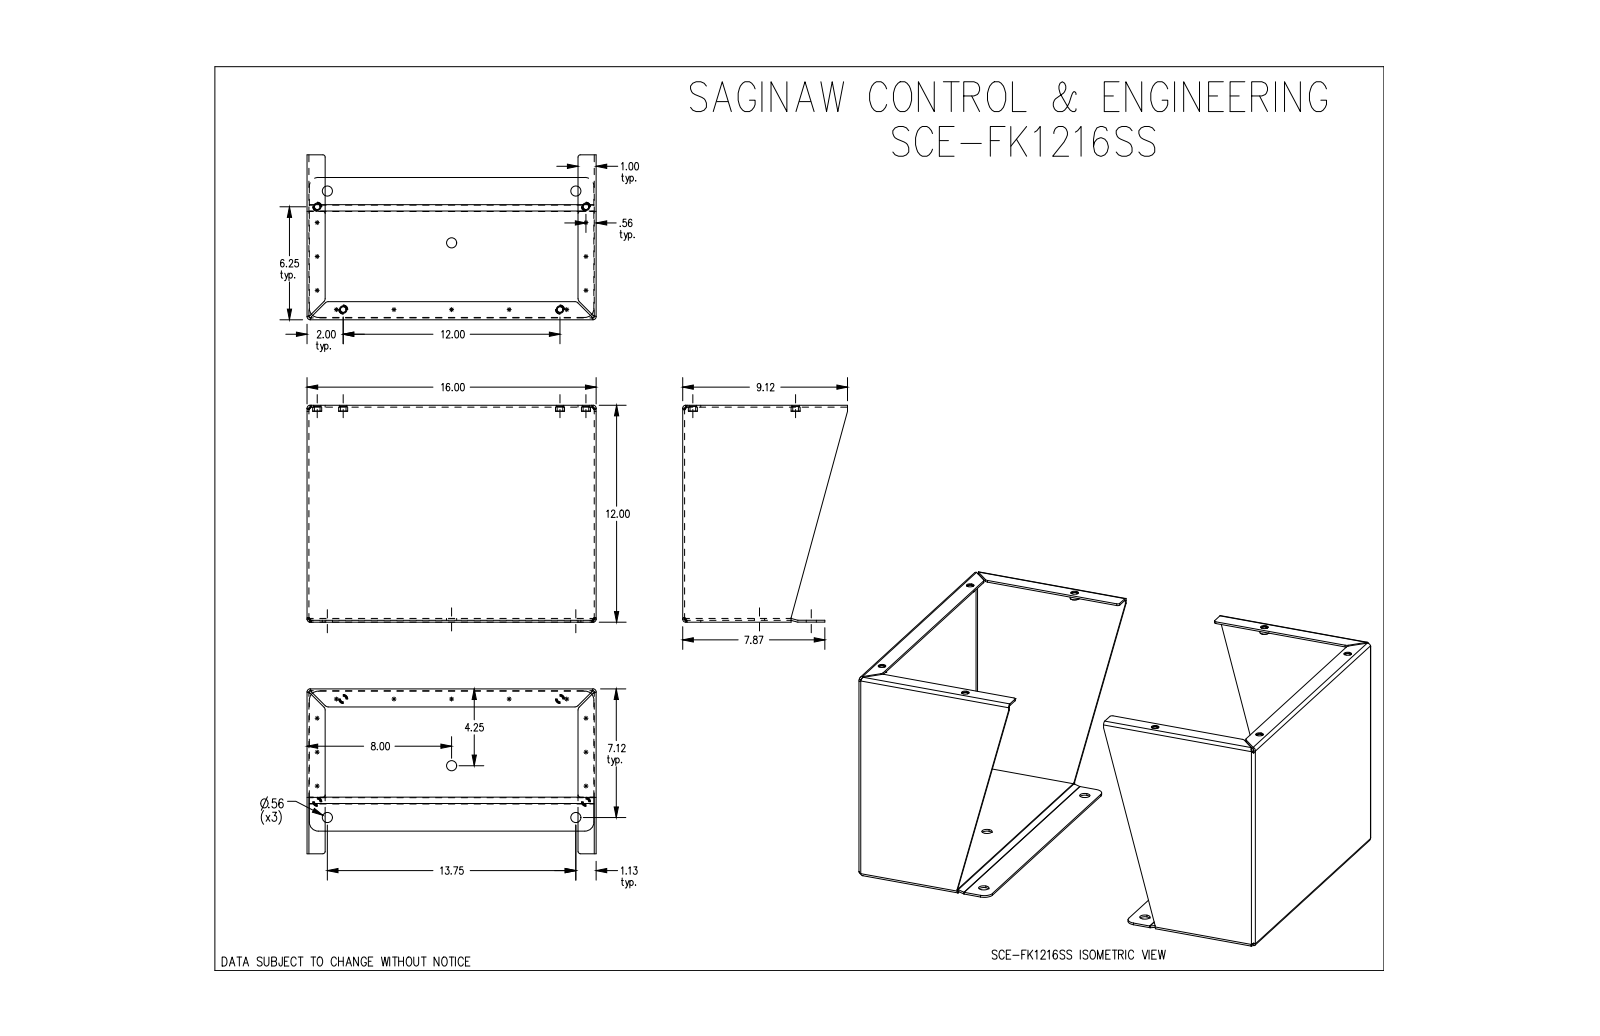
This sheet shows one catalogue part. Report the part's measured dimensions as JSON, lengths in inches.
{"part_name": "SCE-FK1216SS", "step_written_by": "SolidWorks 2019 (CONFIG_CONTROL_DESIGN)", "units": "inches", "bodies": {"solids": 12, "faces": 286, "planar": 120, "cylindrical": 110, "other": 56}, "overall_size": [24, 16, 12], "volume_in3": 112.3, "surface_area_in2": 2194, "round_holes": [[0.312, 8], [0.413, 8], [0.563, 6]], "round_bosses_or_shafts": [[0.5, 8], [0.412, 8]], "partial_cylinders_radius": [[0.166, 16], [0.062, 12], [0.125, 8], [0.22, 8], [0.5, 8], [0.063, 6]], "face_to_face_distances": [0.104, 23.896, 15.896, 23.792, 24, 15.792, 16, 11.792, 11.896, 0.101], "hole_center_spacings": [1.035, 5.866, 6.614, 7.043, 7.449, 7.701, 10.646, 14.38]}
